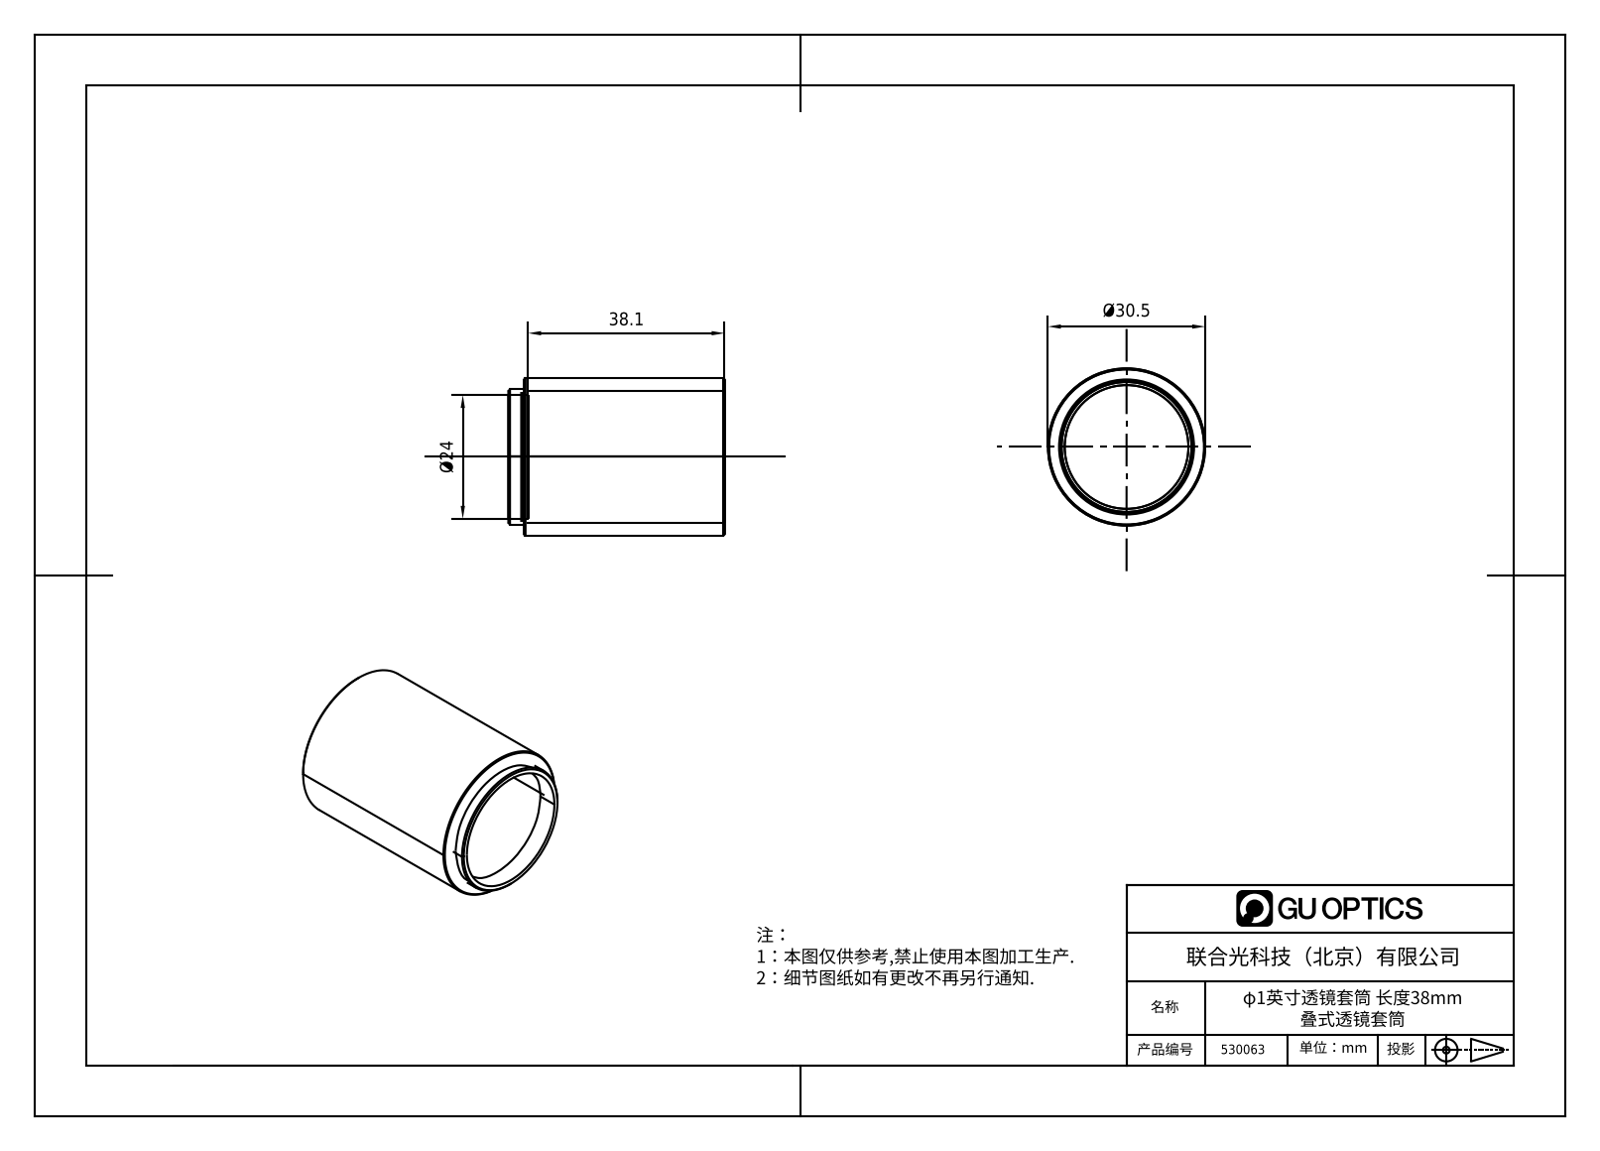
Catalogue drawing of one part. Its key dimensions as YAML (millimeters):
part_name: "1.7.1.10_ZTC-1-1.5_SM1标准型1.5英寸层叠式透镜套筒"
step_written_by: "SolidWorks 2018 (AUTOMOTIVE_DESIGN)"
units: millimeters
bodies: {solids: 0, faces: 34, planar: 11, cylindrical: 12, other: 11}
overall_size: [41.9, 30.5, 30.5]
round_holes:
  - {diameter: 23.01, count: 1}
  - {diameter: 24, count: 1}
  - {diameter: 25.65, count: 1}
round_bosses_or_shafts:
  - {diameter: 30.5, count: 1}
  - {diameter: 26.2, count: 1}
  - {diameter: 25.2, count: 1}
face_to_face_distances: [38.9, 1.19, 37.71, 41.9, 40.71, 3, 1.89, 0.7, 37.01, 40.01]
